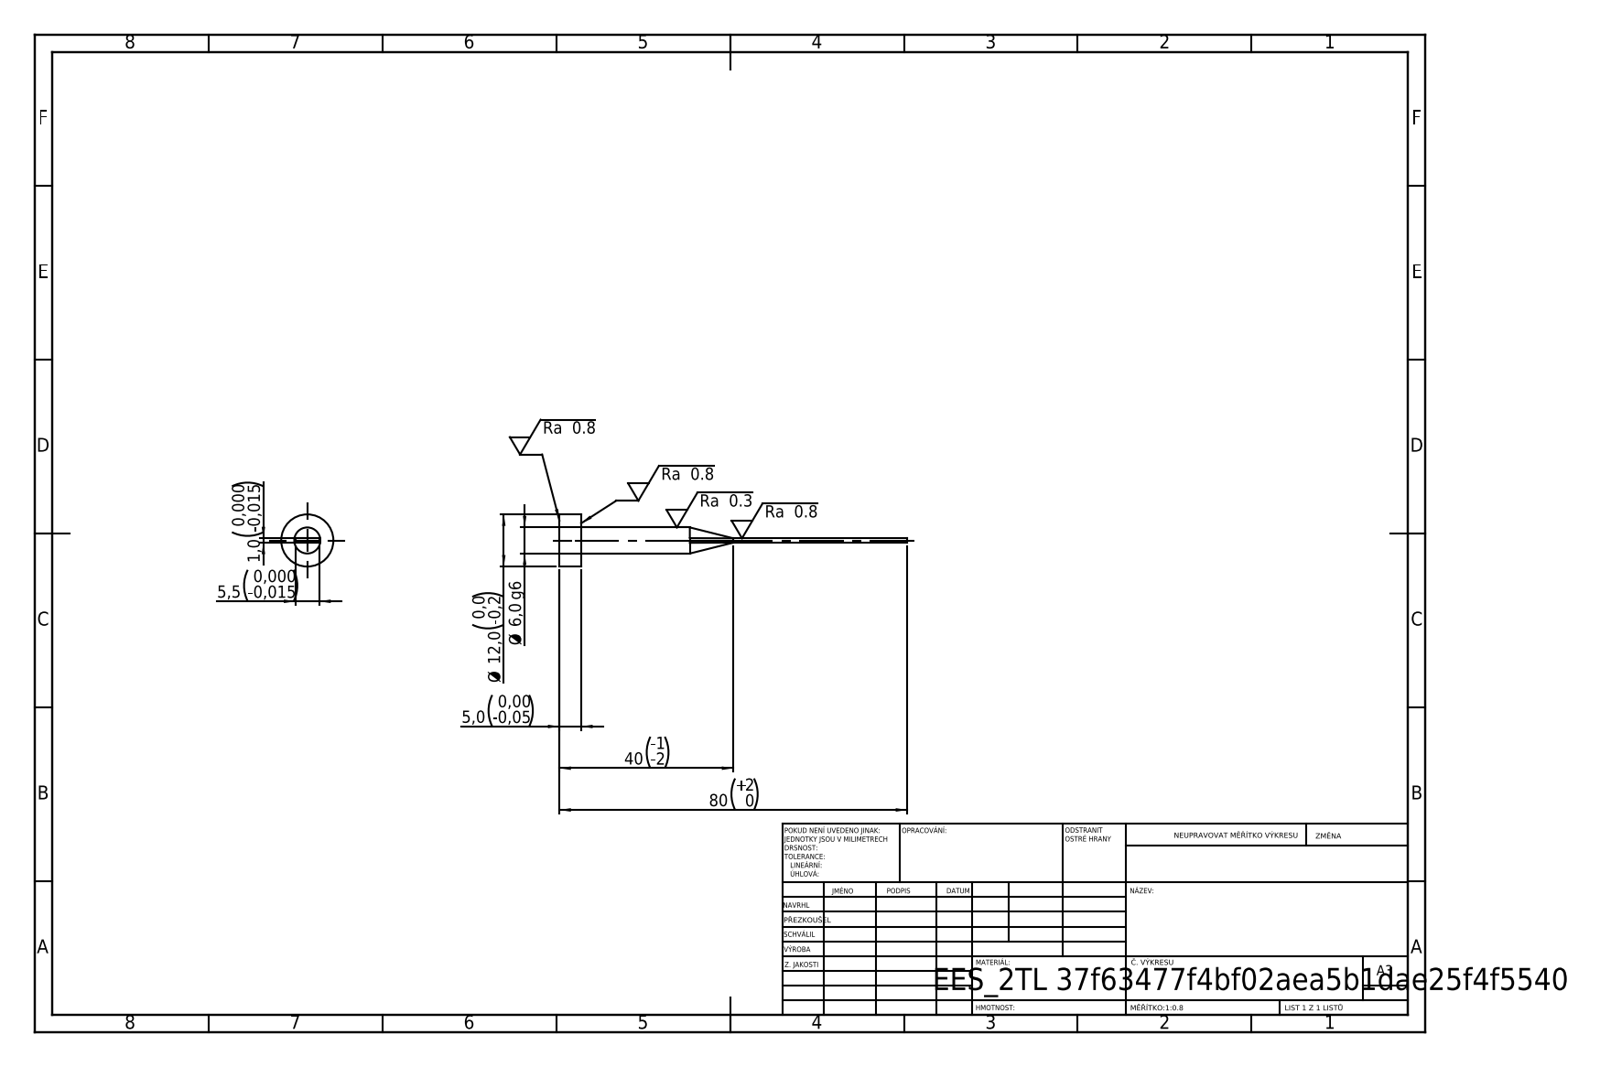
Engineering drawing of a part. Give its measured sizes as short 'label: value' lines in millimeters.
written by: SolidWorks 2019 (CONFIG_CONTROL_DESIGN)
unit: mm
bodies: 1 solid, 15 faces (7 planar, 4 cylindrical, 4 other)
size: 80 × 12 × 12
volume: 1 652 mm³; area: 1 537 mm²
bosses: 1× ⌀12, 1× ⌀6
face distances: 1, 5, 5.5, 80, 75
